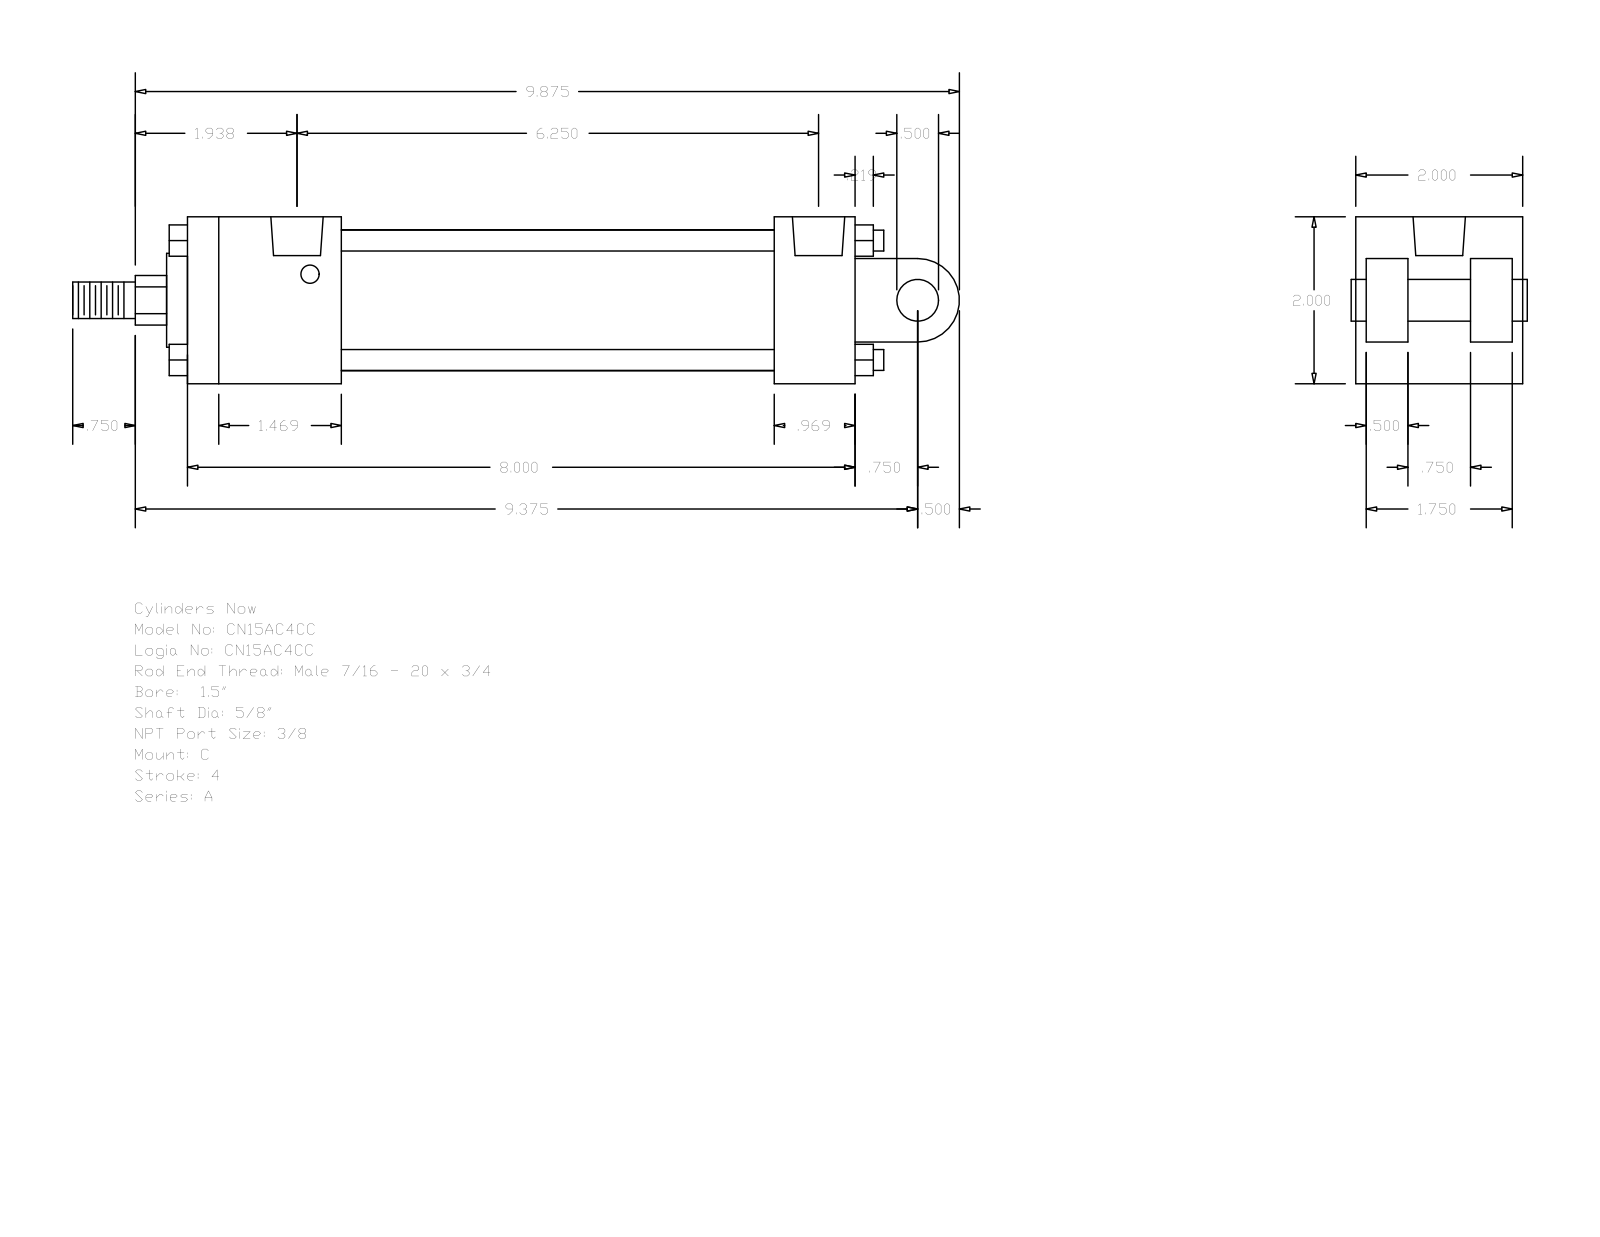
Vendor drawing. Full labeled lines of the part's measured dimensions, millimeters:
Part name (STEP PRODUCT): A_C__0150_0.625
STEP written by: GSSL Pune (CONFIG_CONTROL_DESIGN)
Units: millimetres
Bodies: 0 solids, 135 faces (102 planar, 33 cylindrical, 0 other)
Overall size (bounding box): 269.88 × 50.8 × 50.8
Round holes (diameter × count): ⌀5.56 ×4, ⌀15.93 ×2
Round bosses / shafts (diameter × count): ⌀6.35 ×4, ⌀42.93 ×1, ⌀28.57 ×1, ⌀15.88 ×1, ⌀12.7 ×1, ⌀11.11 ×1
Partial cylindrical surfaces — rounded edges, fillets, slot ends (radius × count): R7.54 ×1, R12.7 ×1
Main face-to-face distances: 50.8, 12.7, 203.19, 34.93, 3.17, 47.63, 15.87, 31.76, 178.59, 24.6
Hole centre spacings: 3.97, 150.81, 154.78, 158.75
